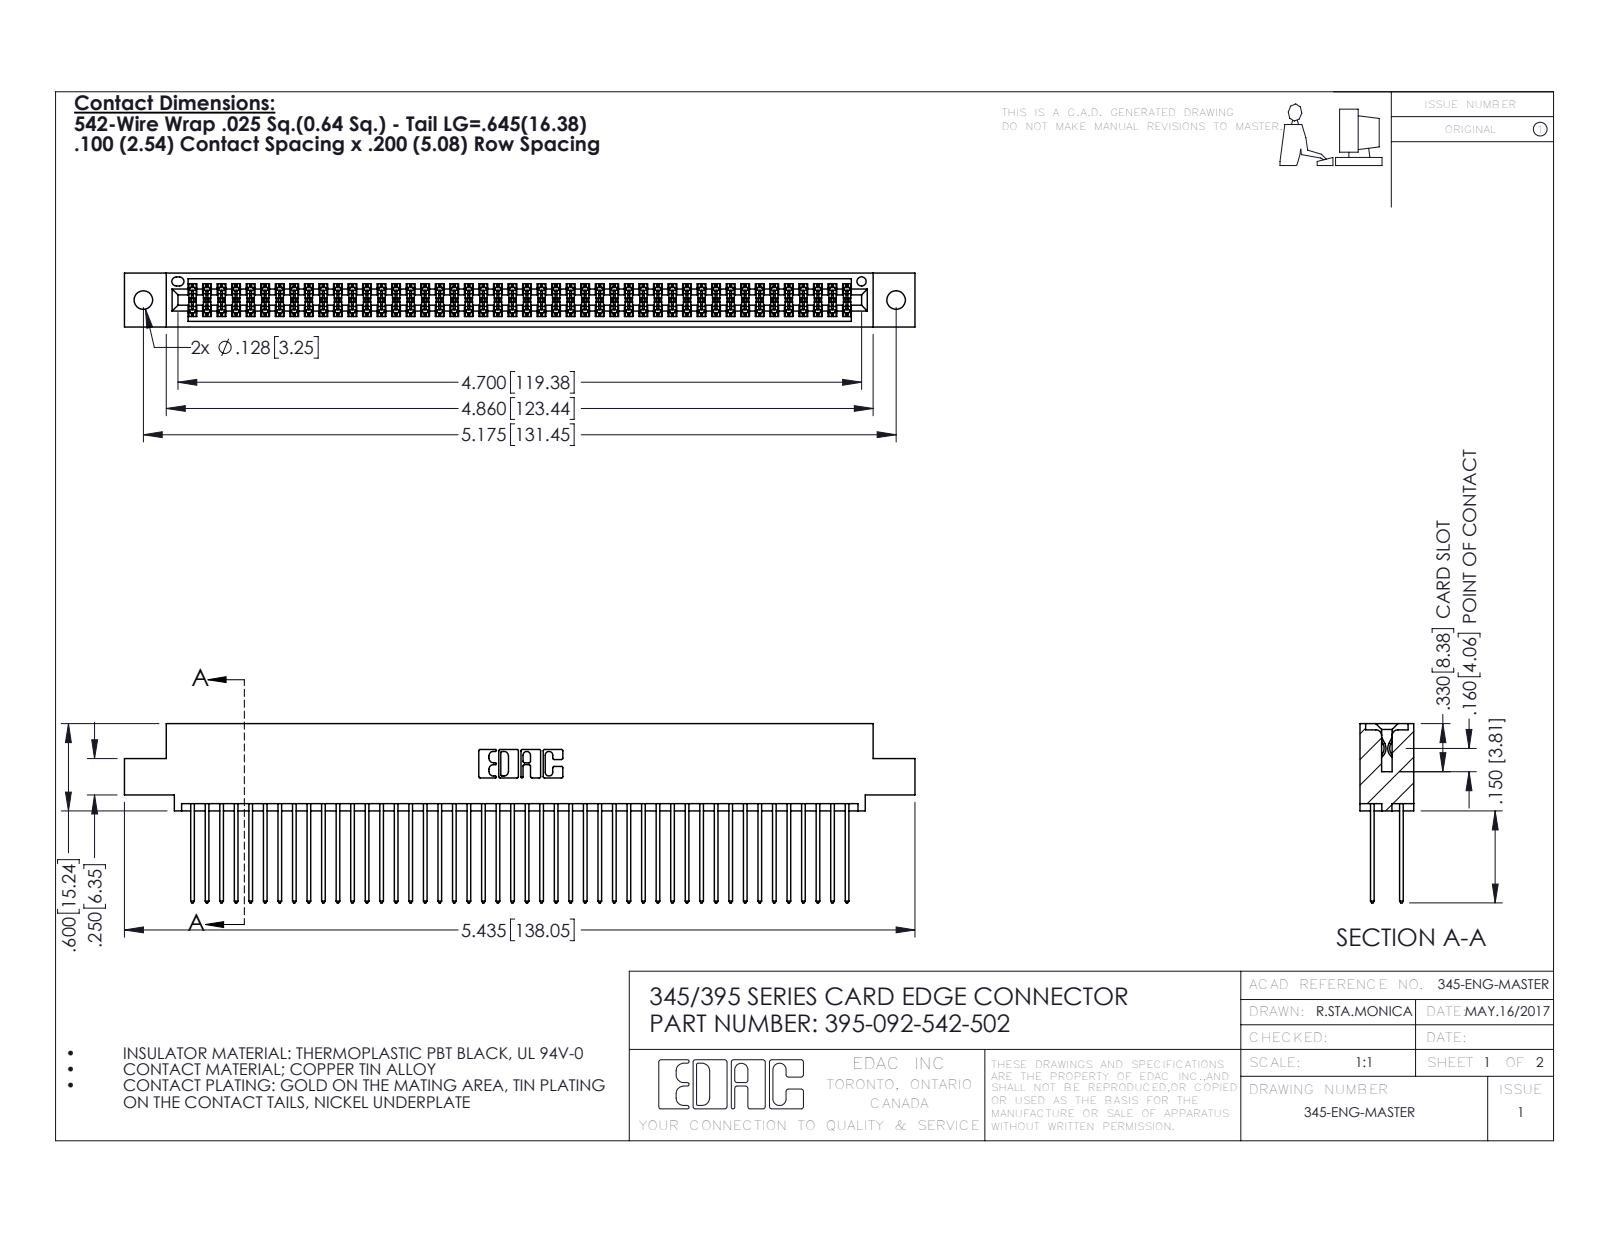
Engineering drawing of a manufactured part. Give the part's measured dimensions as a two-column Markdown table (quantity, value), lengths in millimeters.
| quantity | value |
| --- | --- |
| part name | 345 Part_0.110 Offset - 0.128 Dia; 395-092-542-502; 345-292-001_345-293-142 |
| STEP written by | SolidWorks 2016 (CONFIG_CONTROL_DESIGN) |
| units | millimeters |
| bodies | 93 solids, 4730 faces (3120 planar, 1610 cylindrical, 0 other) |
| overall size | 138 × 31.3 × 9.4 |
| volume | 13 800 mm³ |
| surface area | 22 250 mm² |
| round holes (diameter × count) | 3.3 × 2, 1.6 × 1 |
| partial cylindrical surfaces (radius × count) | 0.2 × 138, 0.3 × 92, 0.3 × 22, 0.2 × 6, 0.8 × 6, 0.7 × 3, 0.4 × 2, 0.5 × 2 |
| main face-to-face distances | 7.6, 1.8, 5.1, 2.5, 6.9, 0.6, 5.7, 9.4, 4.4, 3.8 |
| hole center spacings | 6.9, 125.5, 131.4 |
